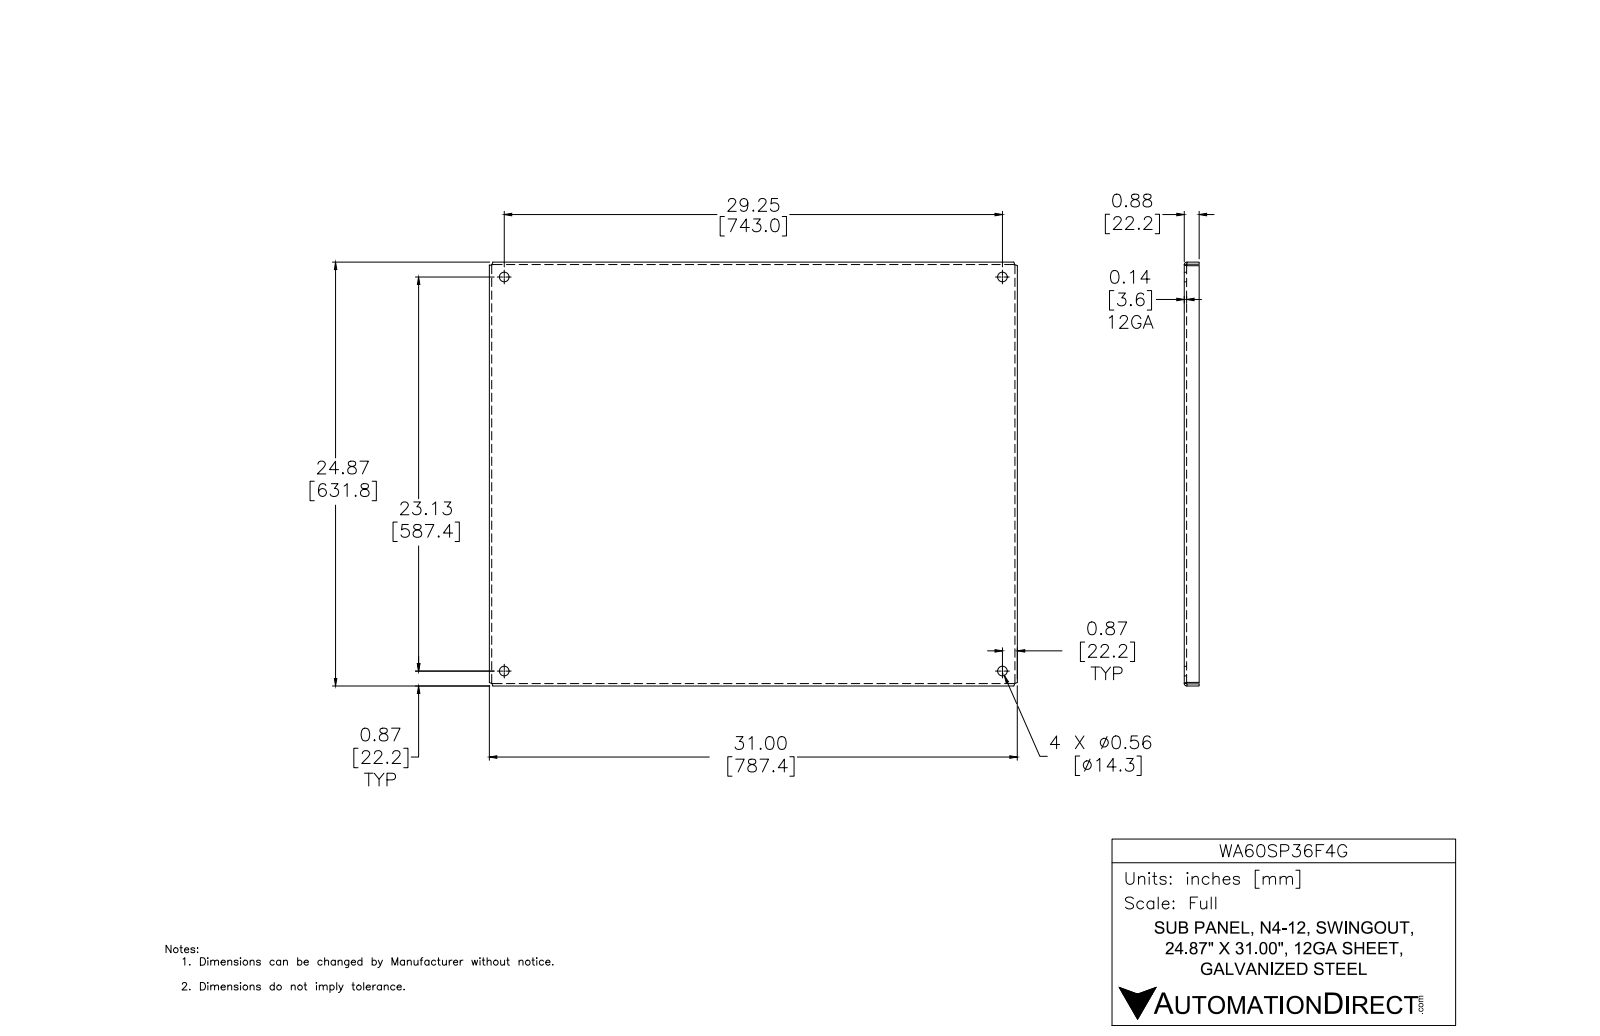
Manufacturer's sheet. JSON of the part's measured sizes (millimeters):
{"part_name": "WA60SP24F3G-WA90SP36F4G", "step_written_by": "Autodesk Inventor 2012 (AUTOMOTIVE_DESIGN)", "units": "millimeters", "bodies": {"solids": 1, "faces": 42, "planar": 22, "cylindrical": 12, "other": 8}, "overall_size": [787.4, 632, 22.2], "volume_mm3": 1310000, "surface_area_mm2": 1108000, "round_holes": [[14.3, 4]], "partial_cylinders_radius": [[0.8, 4], [3.2, 4]], "face_to_face_distances": [2.4, 629.6, 785, 632, 627.2, 787.4, 782.7, 19.8, 22.2, 4.1], "hole_center_spacings": [587.5, 743, 947.2]}
